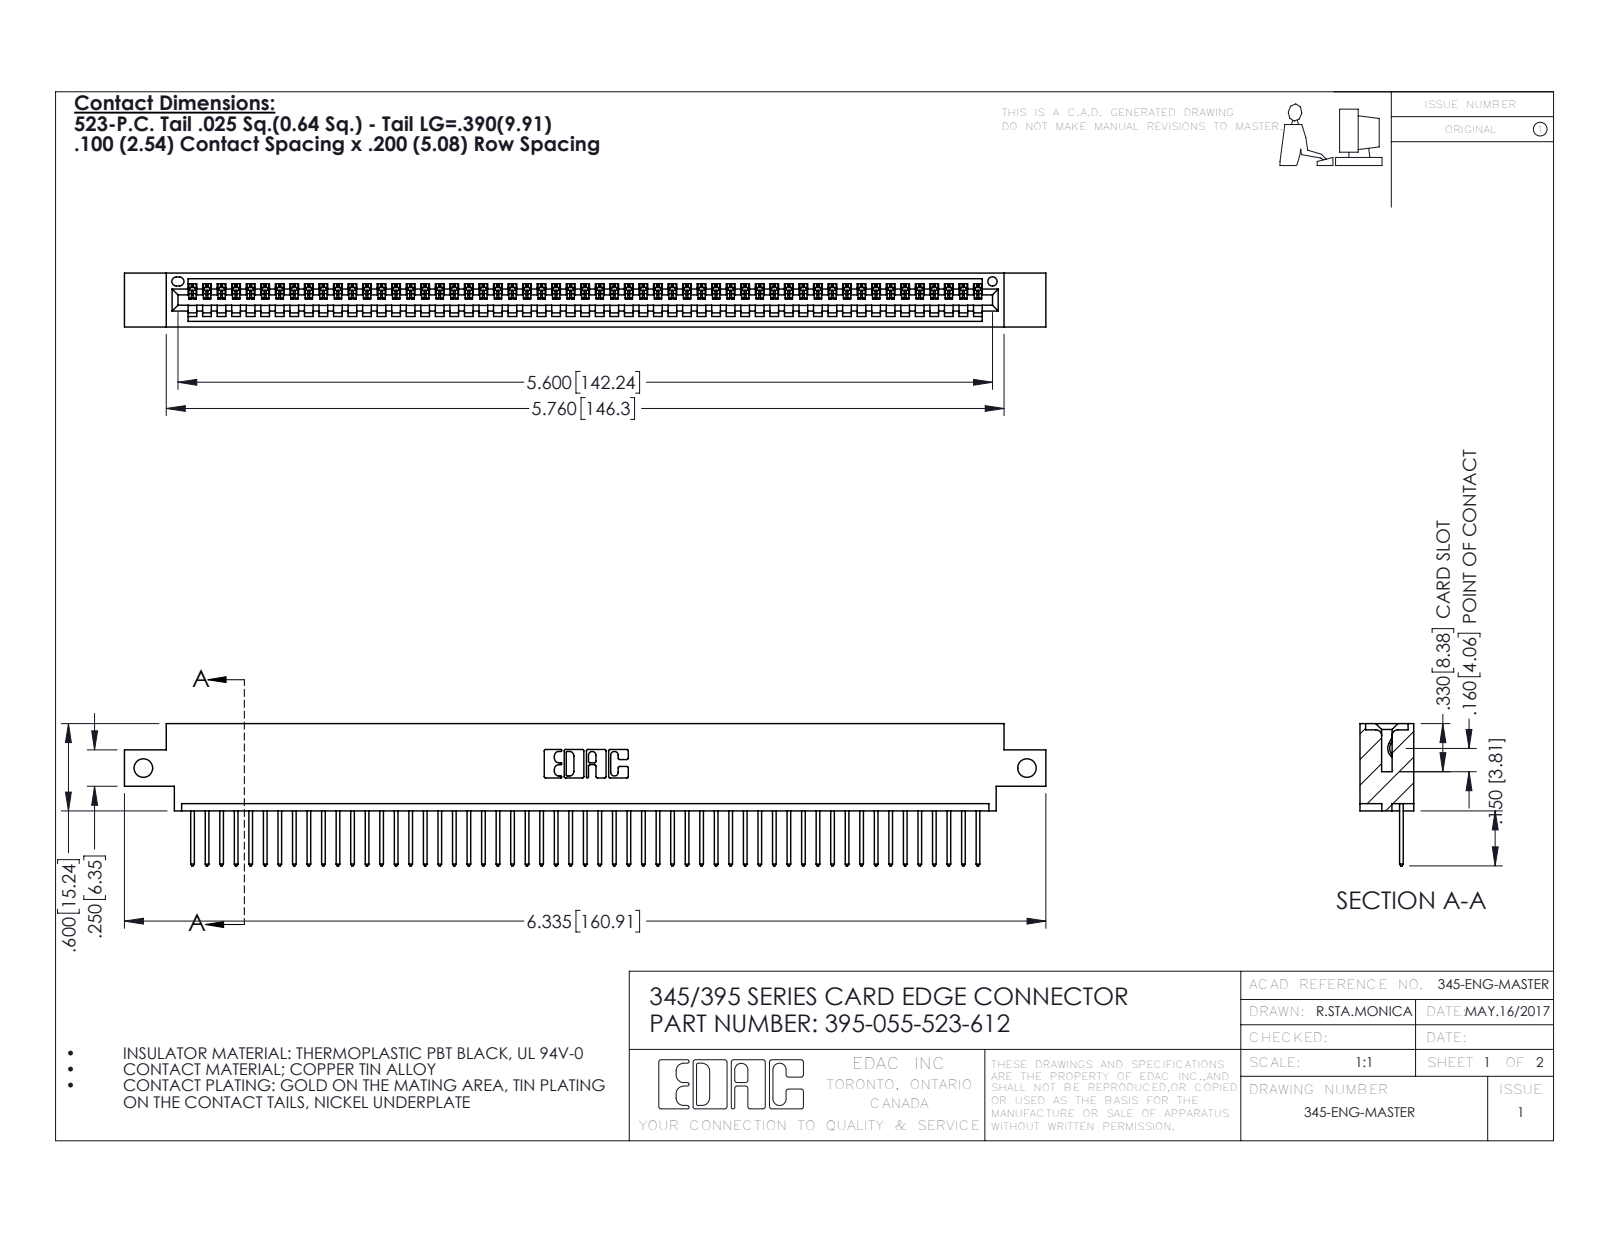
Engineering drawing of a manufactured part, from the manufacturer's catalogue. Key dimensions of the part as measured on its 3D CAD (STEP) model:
Part name (STEP PRODUCT): 345-292-001_345-293-123; 345 Part_0.170 Offset - Side Mount; 395-055-523-612
STEP written by: SolidWorks 2016 (CONFIG_CONTROL_DESIGN)
Units: inches
Bodies: 56 solids, 3320 faces (2284 planar, 1036 cylindrical, 0 other)
Overall size (bounding box): 6.335 × 0.977 × 0.37
Volume: 0.926 in³ · Surface area: 31.59 in²
Round holes (diameter × count): ⌀0.128 ×2, ⌀0.064 ×1
Partial cylindrical surfaces — rounded edges, fillets, slot ends (radius × count): R0.006 ×110, R0.01 ×110, R0.01 ×22, R0.007 ×6, R0.031 ×6, R0.026 ×3, R0.031 ×2, R0.04 ×2
Main face-to-face distances: 0.298, 0.072, 0.37, 0.098, 0.272, 0.025, 0.2, 0.225, 0.175, 0.149
Hole centre spacings: 6.075
